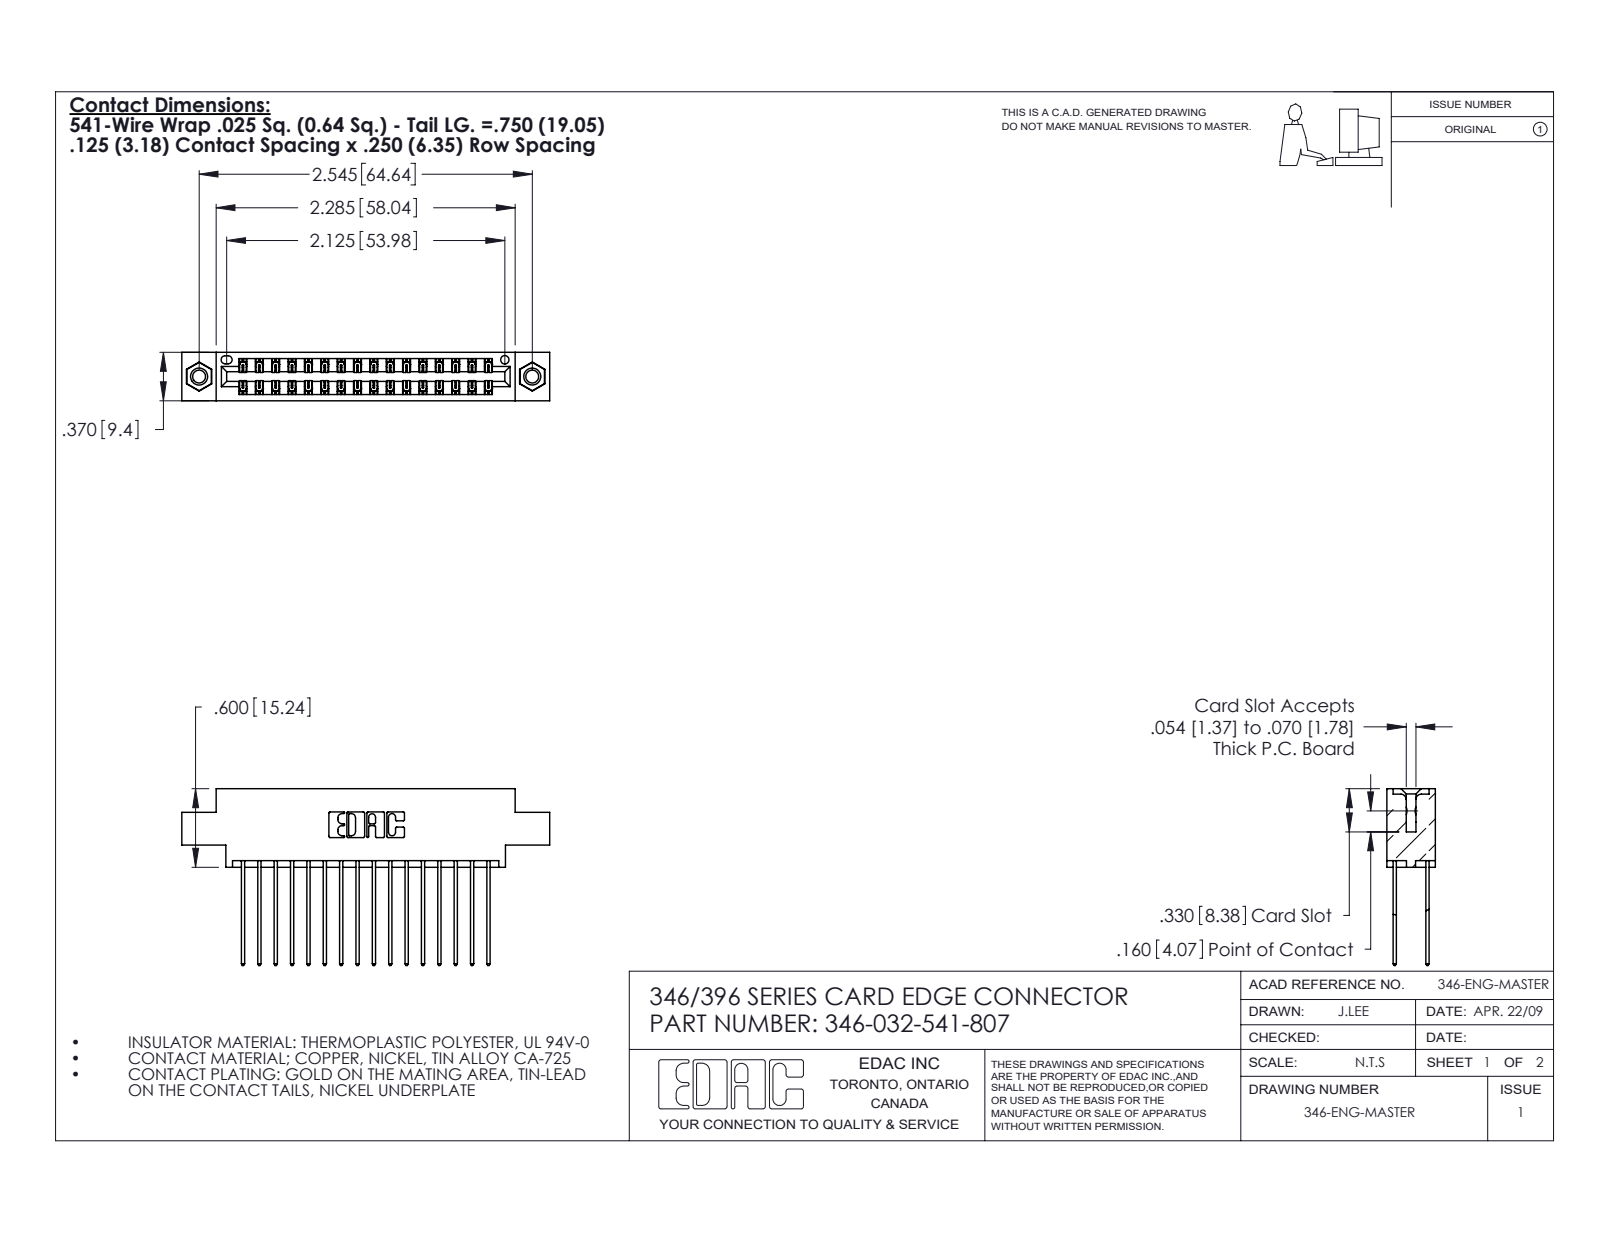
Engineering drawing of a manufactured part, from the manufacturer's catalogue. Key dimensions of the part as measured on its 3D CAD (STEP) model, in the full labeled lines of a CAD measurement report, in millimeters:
Part name (STEP PRODUCT): 346 Part_0.170 Offset - 0.156 Dia-TI; 345-292-001_345-293-141; 346-032-541-807; 345-250-001_345-250-005-103
STEP written by: SolidWorks 2020 (CONFIG_CONTROL_DESIGN)
Units: millimetres
Bodies: 35 solids, 1850 faces (1232 planar, 602 cylindrical, 16 other)
Overall size (bounding box): 71.4 × 34.3 × 9.4
Volume: 6 770 mm³ · Surface area: 9 994 mm²
Round holes (diameter × count): ⌀2.5 ×2, ⌀3.2 ×2, ⌀4 ×2, ⌀1.6 ×1
Round bosses / shafts (diameter × count): ⌀3.9 ×2
Partial cylindrical surfaces — rounded edges, fillets, slot ends (radius × count): R0.2 ×48, R0.3 ×32, R0.3 ×22, R0.2 ×6, R0.8 ×6, R0.7 ×3, R0.4 ×2, R0.6 ×2
Main face-to-face distances: 1.2, 8.2, 6.4, 9.4, 1.8, 7.6, 0.6, 7, 5.6, 3.8
Hole centre spacings: 6.2, 59.4, 64.6
